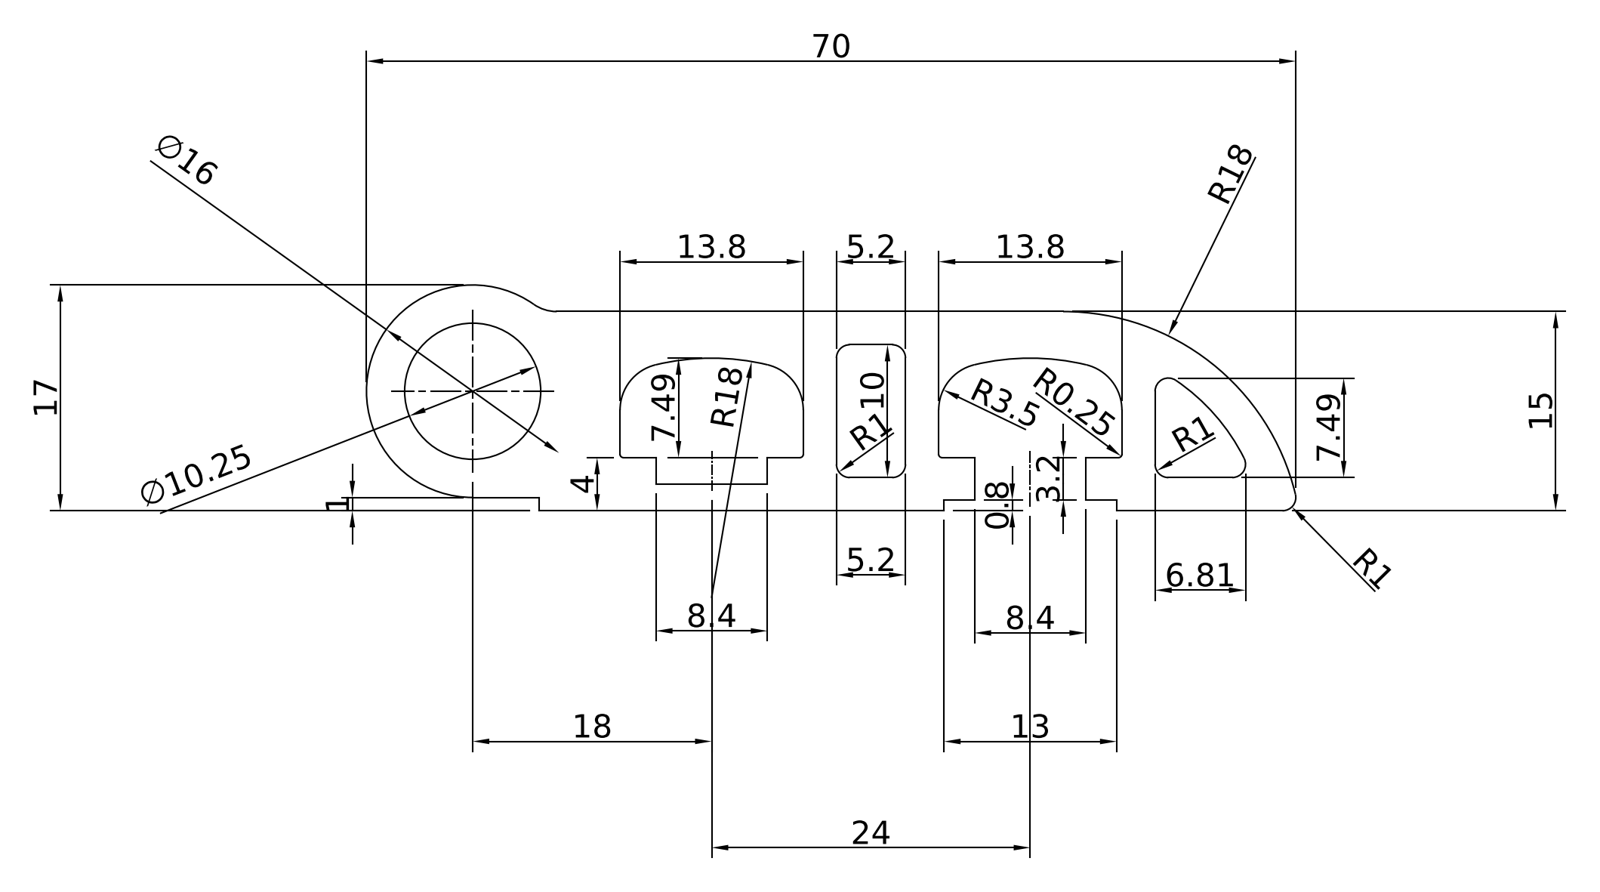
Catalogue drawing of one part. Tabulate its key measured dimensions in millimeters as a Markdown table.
| quantity | value |
| --- | --- |
| part name | BPRCR0000027 |
| STEP written by | Autodesk Inventor 2019 (AUTOMOTIVE_DESIGN) |
| units | millimeters |
| bodies | 1 solid, 53 faces (30 planar, 23 cylindrical, 0 other) |
| overall size | 100 × 70 × 17 |
| volume | 55 722 mm³ |
| surface area | 32 627 mm² |
| round holes (diameter × count) | 10.25 × 1 |
| partial cylindrical surfaces (radius × count) | 1 × 8, 0.25 × 4, 3.5 × 4, 18 × 3, 3 × 1, 8 × 1, 15.5 × 1 |
| main face-to-face distances | 15, 2.5, 2, 5.2, 24, 1.5, 12.5, 18.8, 2.7, 11.1 |
